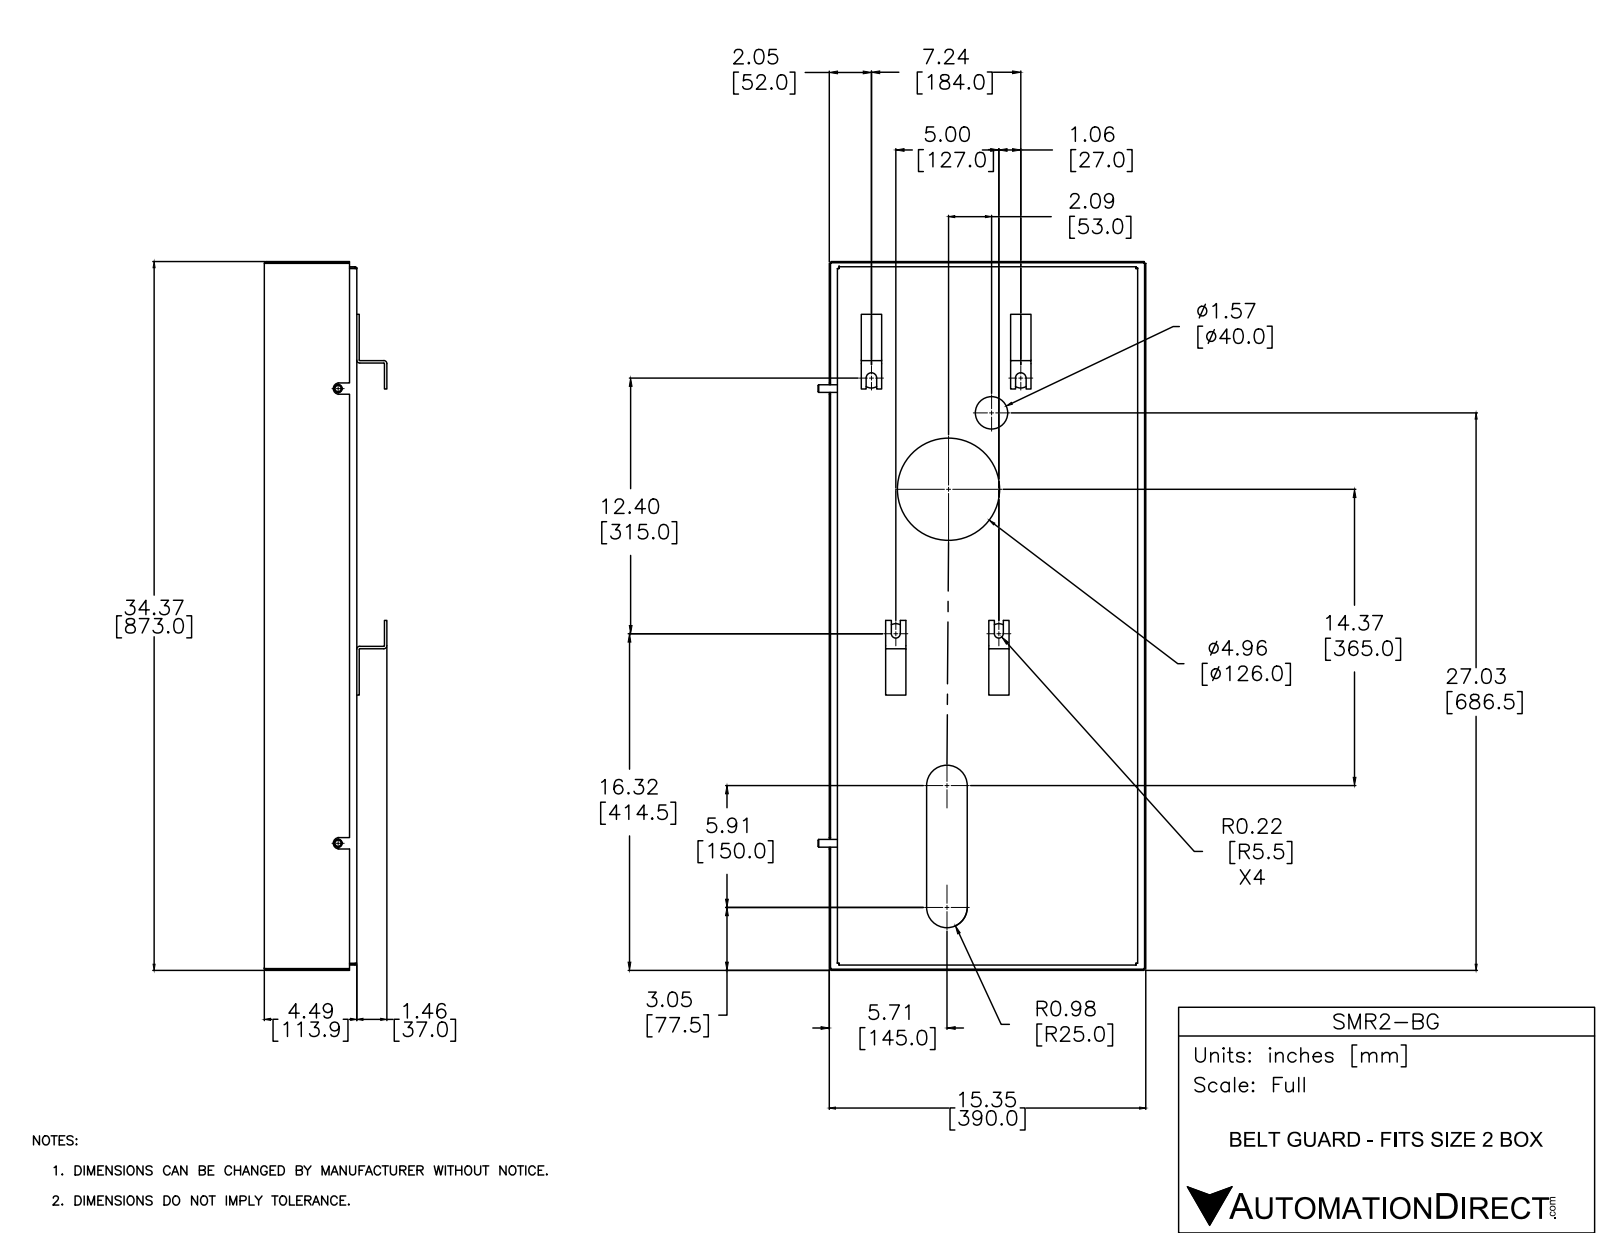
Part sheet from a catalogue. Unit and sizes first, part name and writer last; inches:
Units: inches
Overall size (bounding box): 34.37 × 15.902 × 5.942
Round holes (diameter × count): ⌀0.965 ×4, ⌀0.394 ×2, ⌀1.575 ×1, ⌀4.961 ×1
Round bosses / shafts (diameter × count): ⌀0.374 ×2
Partial cylindrical surfaces — rounded edges, fillets, slot ends (radius × count): R0.029 ×12, R0.088 ×8, R0.147 ×4, R0.217 ×2, R0.256 ×2, R0.276 ×2, R0.984 ×2
Main face-to-face distances: 0.059, 4.427, 4.486, 4.368, 15.295, 0.394, 14.902, 15.354, 15.236, 34.311
Hole centre spacings: 2.208, 4.248, 5, 6.068, 6.432, 6.564, 7.244, 7.421
Volume: 91.42 in³ · Surface area: 3 075 in²
Bodies: 8 solids, 202 faces (122 planar, 60 cylindrical, 20 other)
Part name (STEP PRODUCT): SMR2-BG
STEP written by: SolidWorks 2016 (AUTOMOTIVE_DESIGN)
